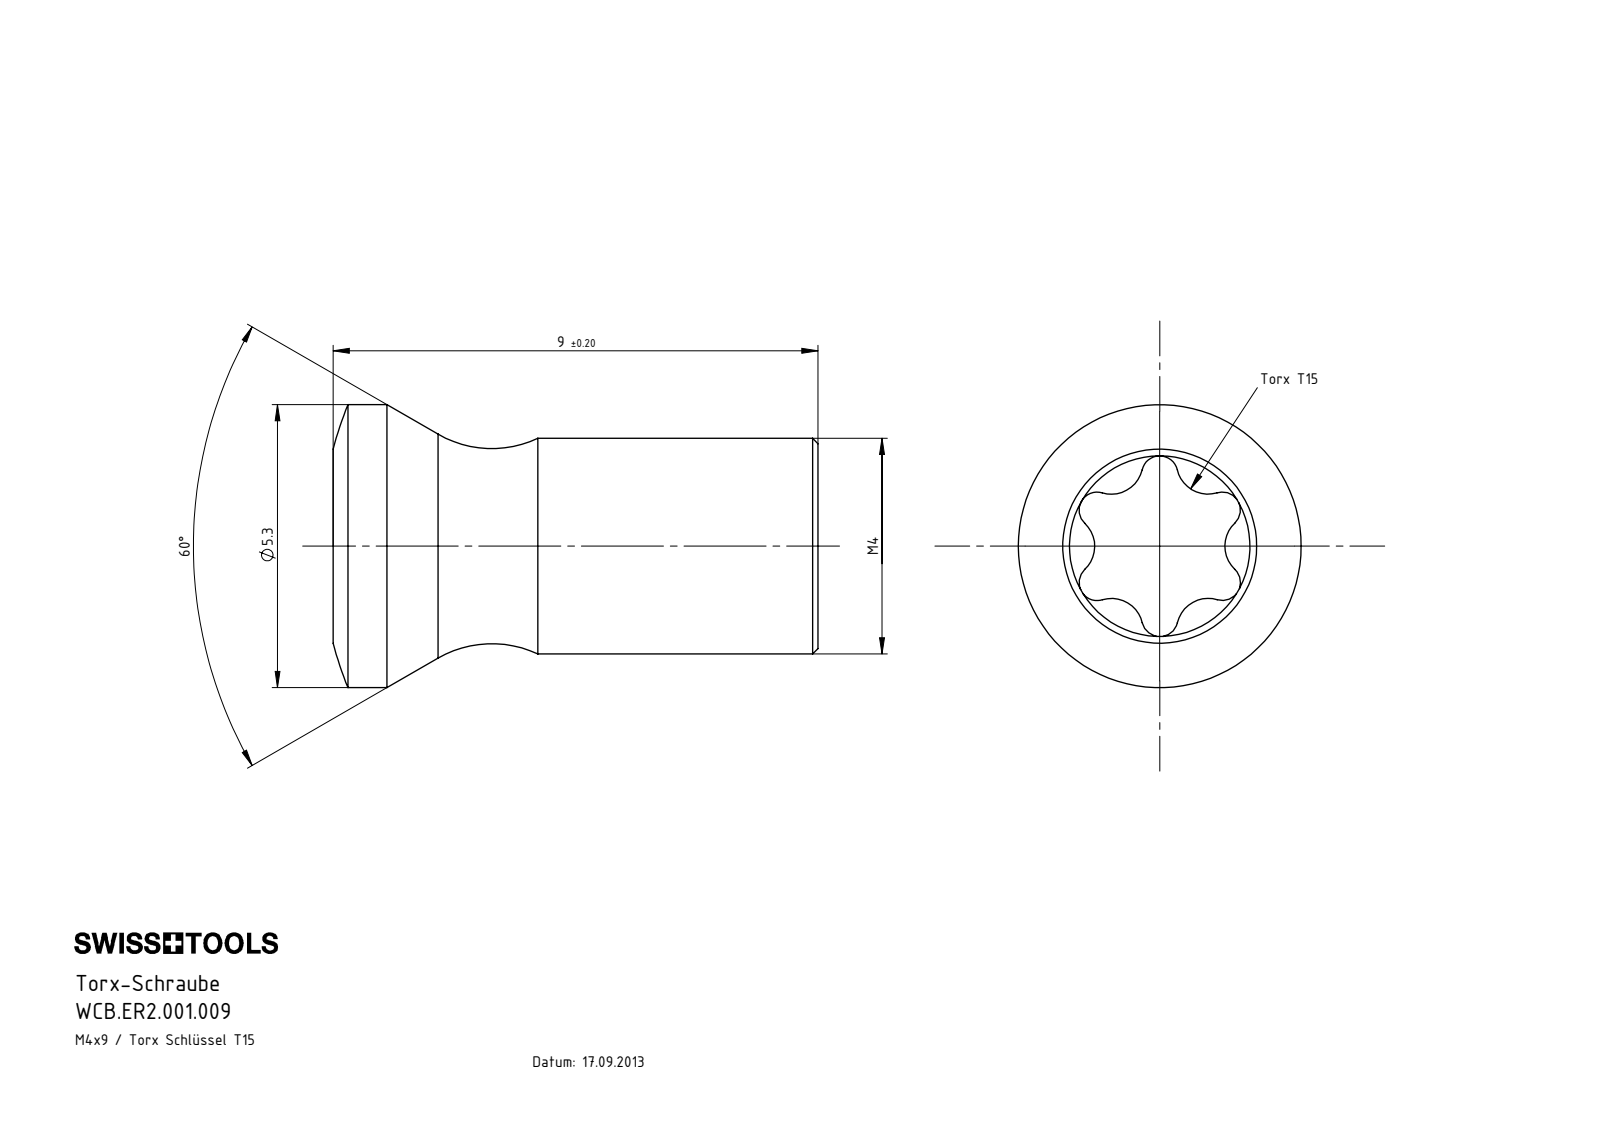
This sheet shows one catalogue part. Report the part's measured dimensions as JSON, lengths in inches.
{"part_name": "WCB.ER2.001.009", "step_written_by": "SolidWorks 2017 (AUTOMOTIVE_DESIGN)", "units": "inches", "bodies": {"solids": 1, "faces": 27, "planar": 3, "cylindrical": 14, "other": 10}, "overall_size": [0.354, 0.207, 0.207], "volume_in3": 0.007, "surface_area_in2": 0.251, "round_bosses_or_shafts": [[0.207, 1], [0.157, 1]], "partial_cylinders_radius": [[0.013, 6], [0.023, 6]], "face_to_face_distances": [0.299, 0.055, 0.354]}
